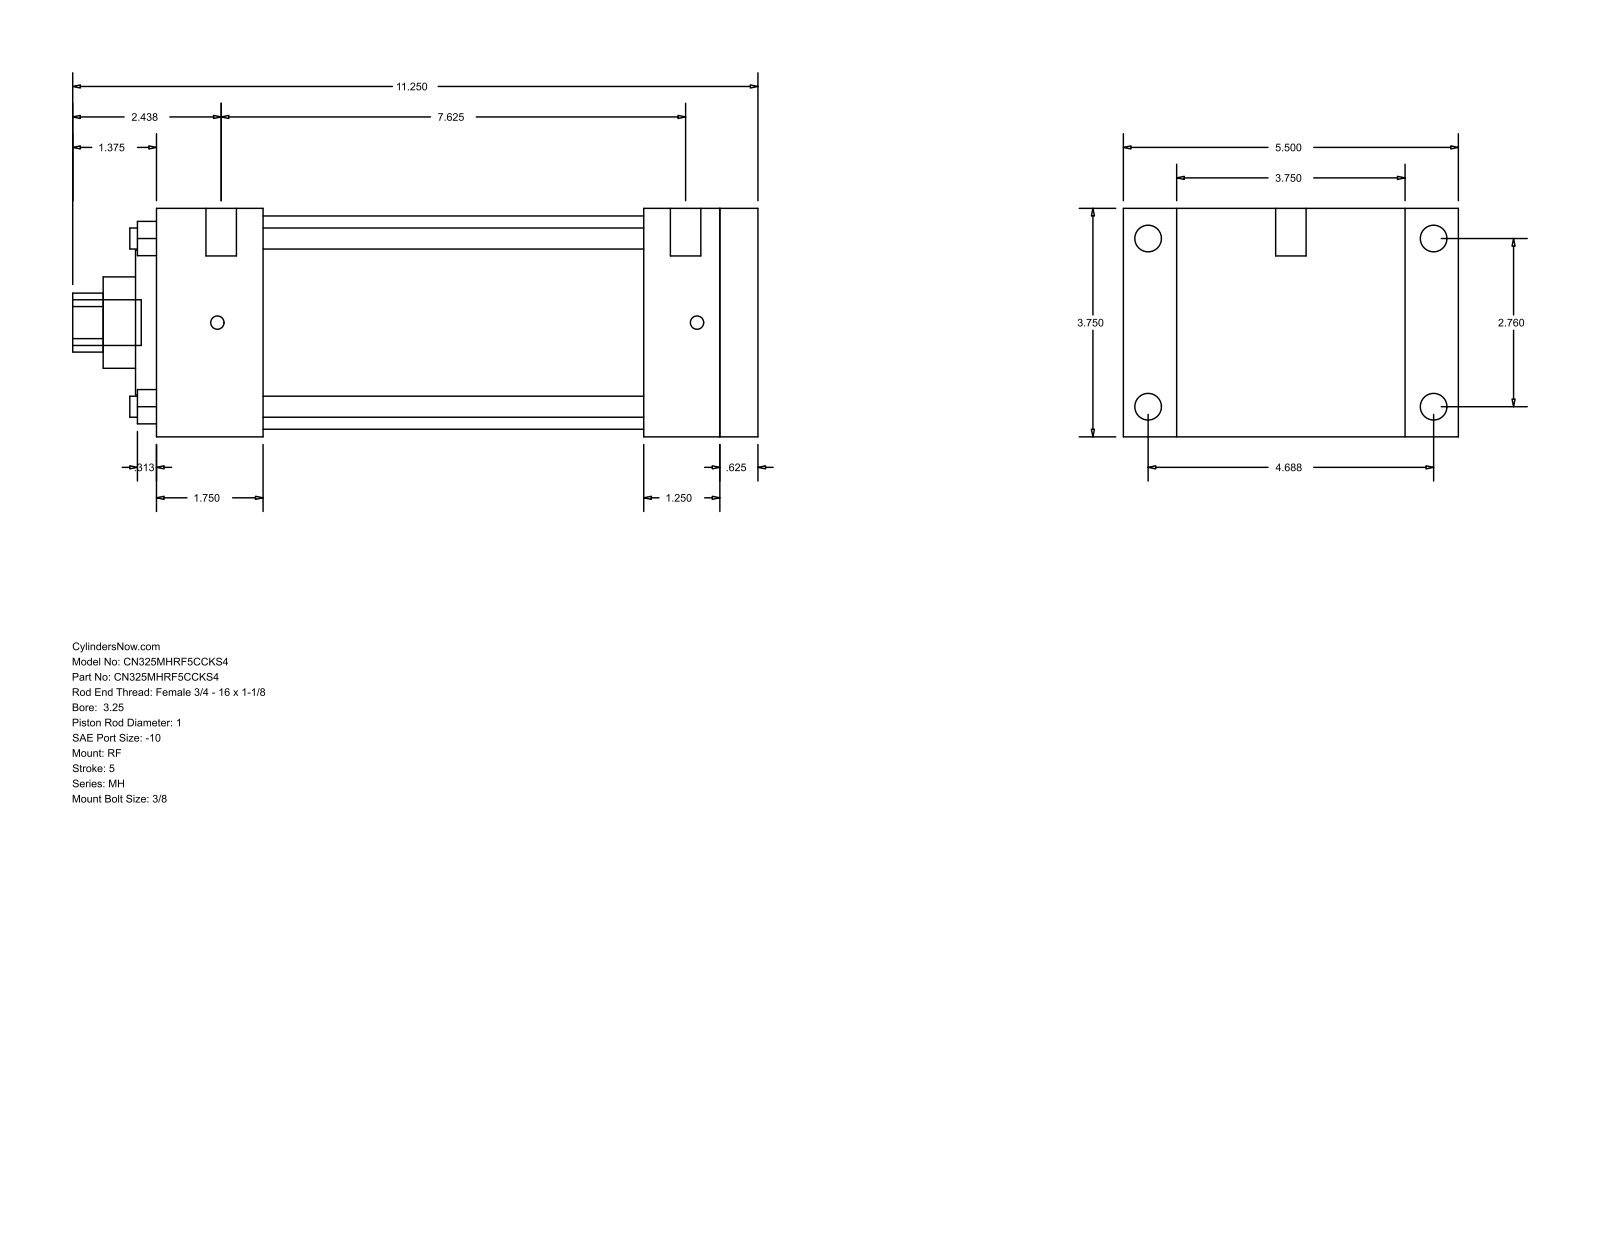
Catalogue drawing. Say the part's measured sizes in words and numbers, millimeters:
The part is named "MH_RF__0325_1". Its 3-D file was written by "GSSL Pune (CONFIG_CONTROL_DESIGN)". It is 0 solids with 94 faces: 65 planar, 29 cylindrical and 0 other. Overall it measures 285.75 by 139.7 by 95.25 millimeters. Round holes: 4 of diameter 8.76, 1 of diameter 25.4, 1 of diameter 38.1, 1 of diameter 60.33, 1 of diameter 88.9. Round bosses or shafts: 4 of diameter 11.13, 4 of diameter 5.56, 2 of diameter 12.7, 1 of diameter 19.05. Partial cylindrical surfaces (rounded edges, fillets, slot ends): 1 of radius 12.29. The main face-to-face distances are 95.24, 250.83, 15.87, 234.96, 22.23, 117.47, 44.46, 190.5, 206.37, 203.2. The hole center spacings are 49.57, 70.1, 99.14.
